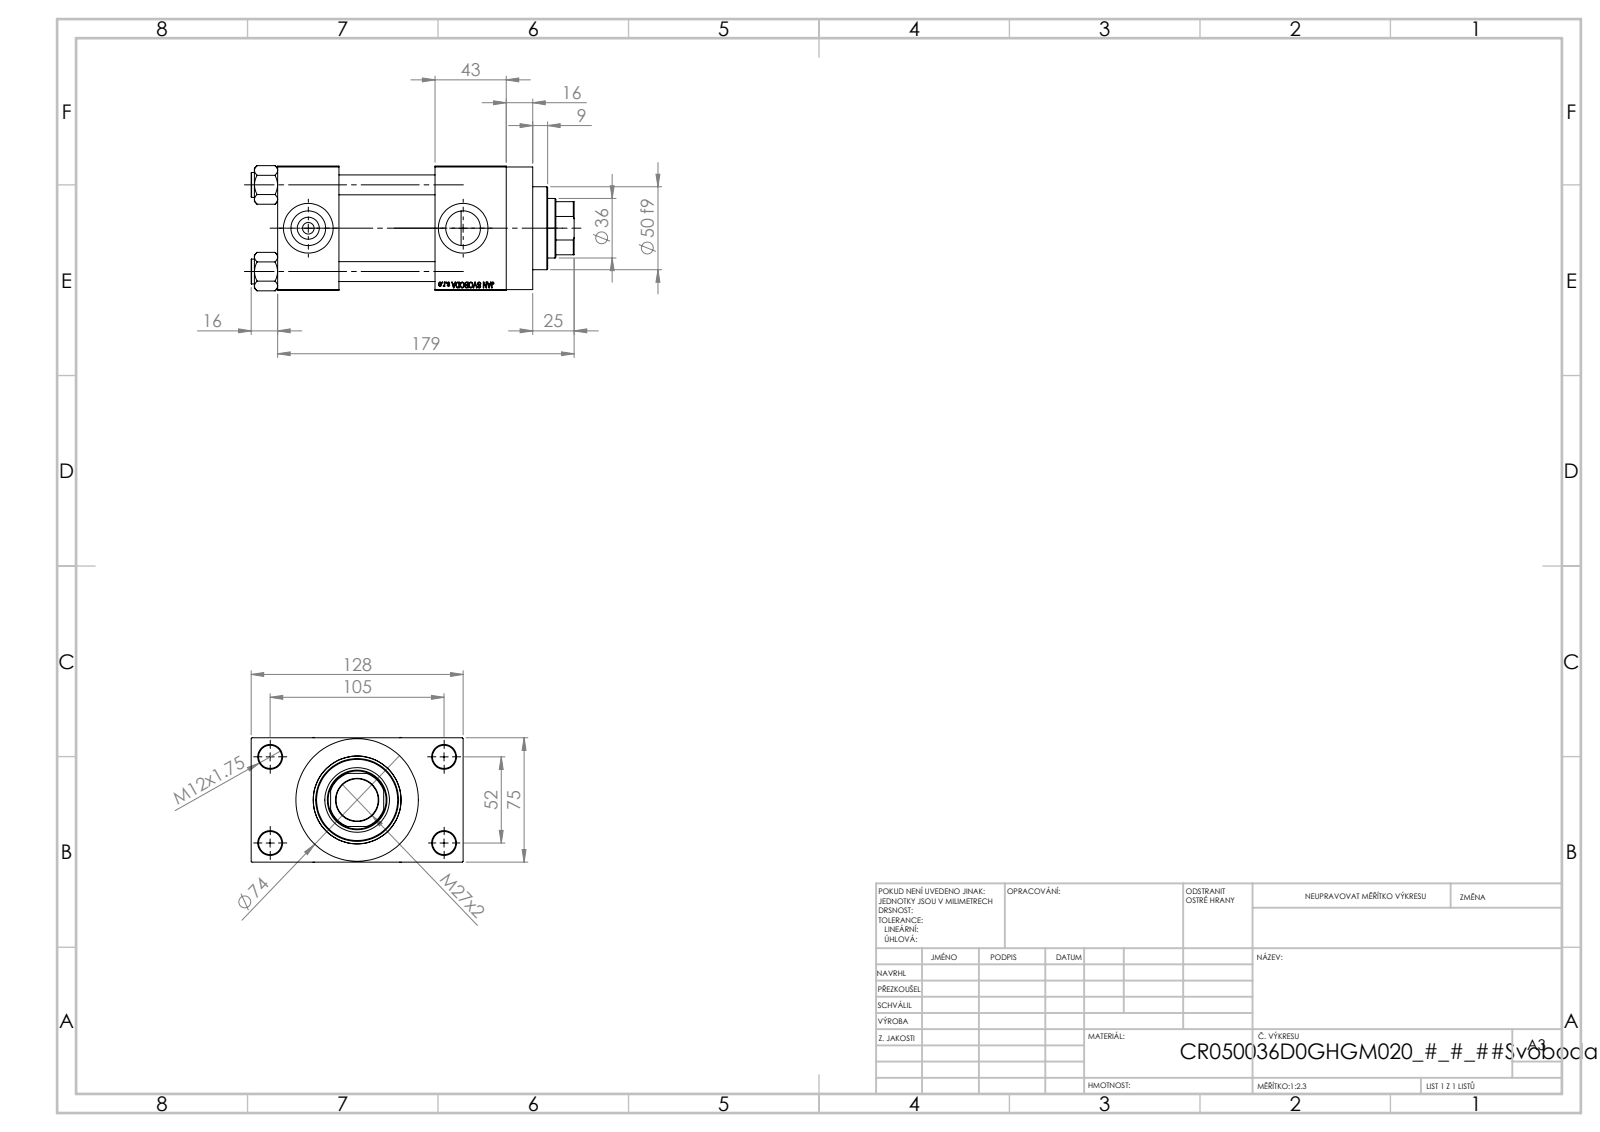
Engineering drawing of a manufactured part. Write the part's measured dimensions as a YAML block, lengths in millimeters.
part_name: "NUT_M5_D; V215CR_VCP_D; V215_VC_A; V215CR_D_Body (+1 more)"
step_written_by: "SolidWorks 2019 (CONFIG_CONTROL_DESIGN)"
units: millimeters
bodies: {solids: 11, faces: 1103, planar: 497, cylindrical: 88, other: 518}
overall_size: [195, 128, 75.54]
volume: 817313
surface_area: 175532
round_holes:
  - {diameter: 12, count: 4}
  - {diameter: 14, count: 4}
  - {diameter: 7, count: 2}
  - {diameter: 20.96, count: 2}
  - {diameter: 30, count: 2}
  - {diameter: 25.5, count: 1}
  - {diameter: 36, count: 1}
  - {diameter: 39, count: 1}
  - {diameter: 41, count: 1}
  - {diameter: 53, count: 1}
round_bosses_or_shafts:
  - {diameter: 15, count: 4}
  - {diameter: 74, count: 1}
  - {diameter: 56, count: 1}
  - {diameter: 50, count: 1}
partial_cylinders:
  - {radius: 17.5, count: 1}
face_to_face_distances: [75, 58, 37, 95, 26.5, 43, 138, 101, 101.5, 16]
hole_center_spacings: [26.35, 36.98, 52.3, 58.43, 58.59, 78.65, 94.37, 52]
